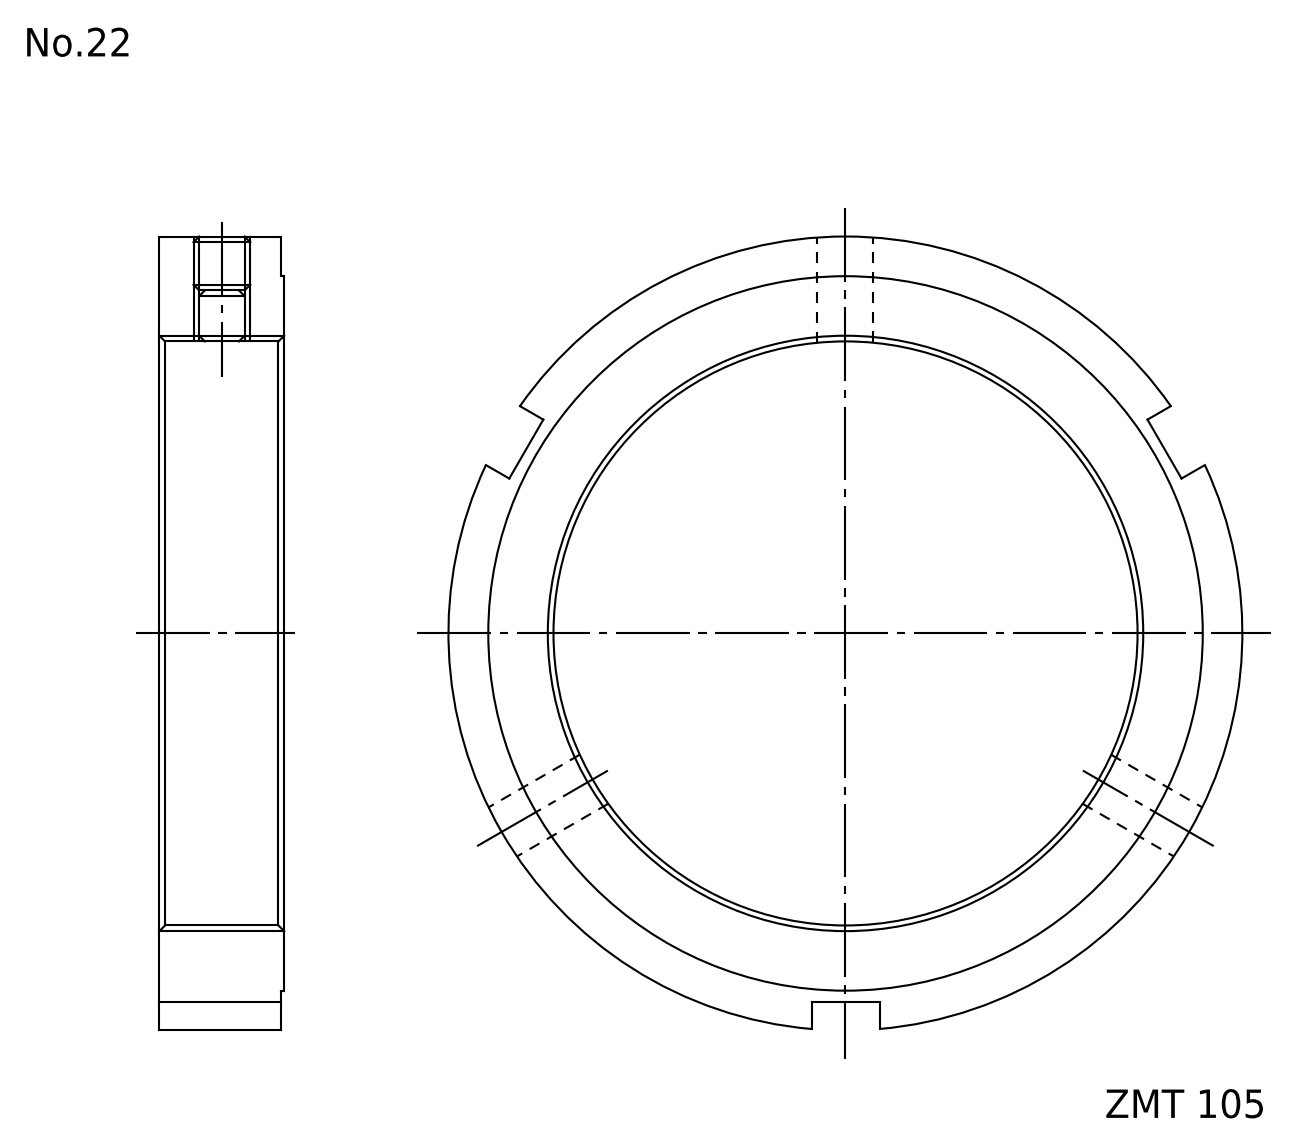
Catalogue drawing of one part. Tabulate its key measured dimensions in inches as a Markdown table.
| quantity | value |
| --- | --- |
| part name | FKD ZMT105 |
| STEP written by | Autodesk Inventor 2011 (AUTOMOTIVE_DESIGN) |
| units | inches |
| bodies | 1 solid, 20 faces (12 planar, 8 cylindrical, 0 other) |
| overall size | 5.512 × 5.502 × 0.866 |
| volume | 8.544 in³ |
| surface area | 49.12 in² |
| round holes (diameter × count) | 0.33 × 3, 4.134 × 1 |
| round bosses / shafts (diameter × count) | 5.512 × 1, 4.961 × 1 |
| main face-to-face distances | 0.866, 0.02, 0.846, 0.472 |
